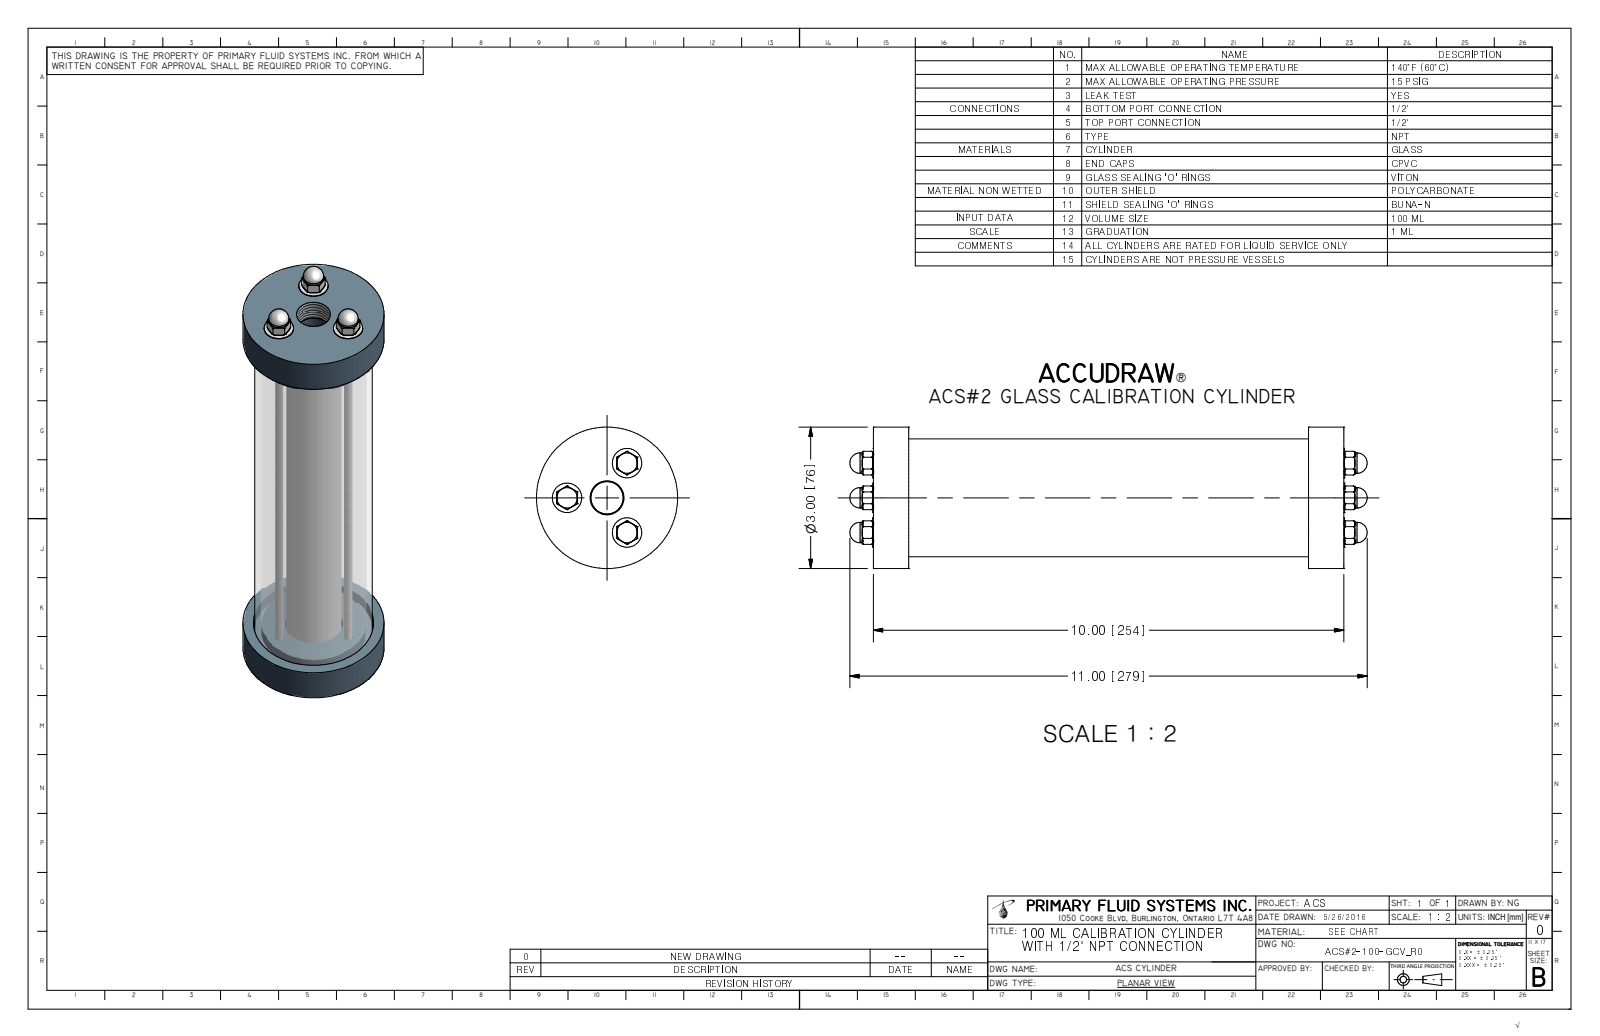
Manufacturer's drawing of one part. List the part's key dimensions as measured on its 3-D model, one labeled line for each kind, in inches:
Part name (STEP PRODUCT): ACS#2-100-GCV_R0; ACS-3-100-POLY_R3; ACS-2-100-PC_R6; ACS-1-100-A_R0 (+3 more)
STEP written by: Autodesk Inventor 2009 (AUTOMOTIVE_DESIGN)
Units: inches
Bodies: 19 solids, 429 faces (38 planar, 41 cylindrical, 350 other)
Overall size (bounding box): 11 × 3 × 3
Volume: 20.05 in³ · Surface area: 287.6 in²
Round holes (diameter × count): ⌀0.18 ×3, ⌀0.201 ×3, ⌀0.281 ×3, ⌀1.071 ×1, ⌀1.22 ×1, ⌀2.25 ×1, ⌀2.55 ×1
Round bosses / shafts (diameter × count): ⌀0.625 ×3, ⌀0.187 ×3, ⌀3 ×1, ⌀2.5 ×1, ⌀2.2 ×1, ⌀1.181 ×1, ⌀0.93 ×1
Main face-to-face distances: 9.25, 0.75, 10, 8.5, 0.475, 0.275, 8.775, 9.525, 0.762, 9.262
Hole centre spacings: 0.85, 1.472, 1.472
